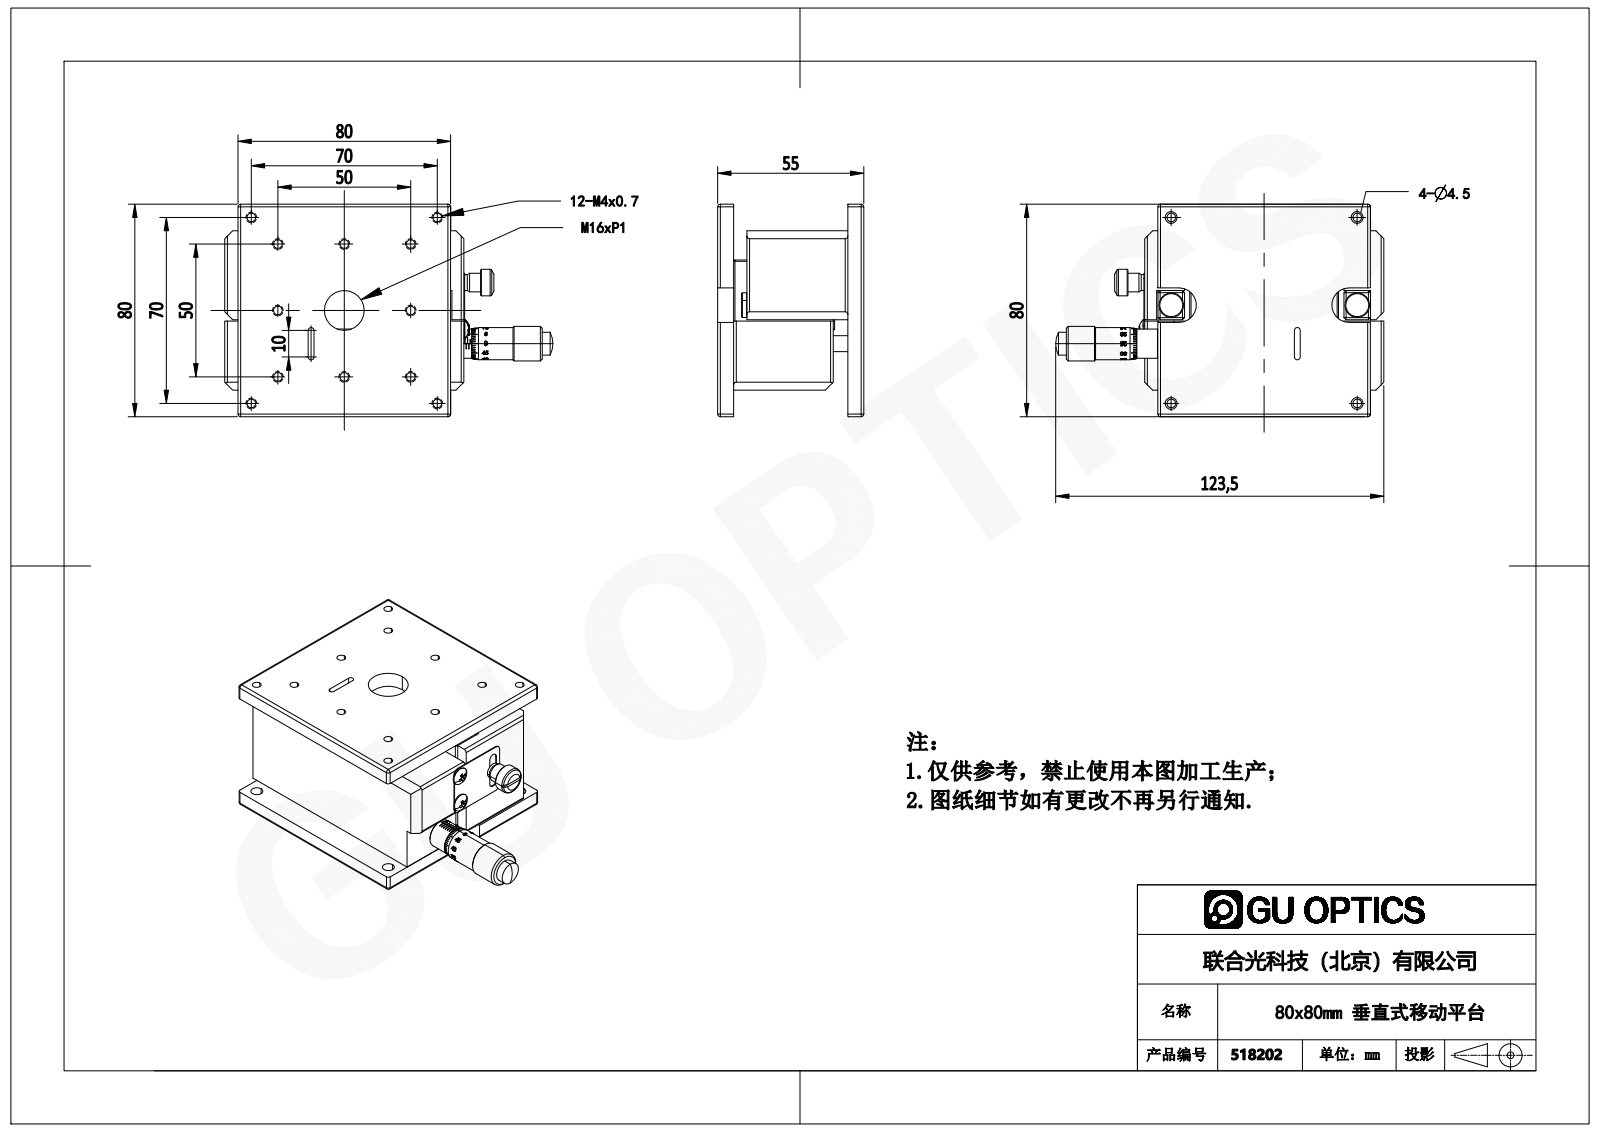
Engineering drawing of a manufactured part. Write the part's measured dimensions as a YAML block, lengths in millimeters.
part_name: "518202"
step_written_by: "SolidWorks 2020 (CONFIG_CONTROL_DESIGN)"
units: millimeters
bodies: {solids: 3, faces: 559, planar: 309, cylindrical: 178, other: 72}
overall_size: [111.5, 80, 45]
volume: 169410
surface_area: 62145
round_holes:
  - {diameter: 3.24, count: 17}
  - {diameter: 2.46, count: 12}
  - {diameter: 3.5, count: 12}
  - {diameter: 6, count: 12}
  - {diameter: 5, count: 9}
  - {diameter: 3, count: 8}
  - {diameter: 4.4, count: 8}
  - {diameter: 2.01, count: 6}
  - {diameter: 2.46, count: 6}
  - {diameter: 2.5, count: 6}
  - {diameter: 1.57, count: 4}
  - {diameter: 4.5, count: 4}
round_bosses_or_shafts:
  - {diameter: 6, count: 2}
  - {diameter: 4, count: 2}
  - {diameter: 3.4, count: 2}
  - {diameter: 2, count: 2}
  - {diameter: 10, count: 1}
  - {diameter: 3, count: 1}
partial_cylinders:
  - {radius: 1, count: 11}
  - {radius: 2, count: 4}
  - {radius: 1.75, count: 2}
face_to_face_distances: [6, 39, 45, 33, 33.5, 23, 6.5, 5.5, 0.5, 11.5]
hole_center_spacings: [25, 35, 26.93, 35.36, 36.4, 43.01, 49.5, 54.65]
